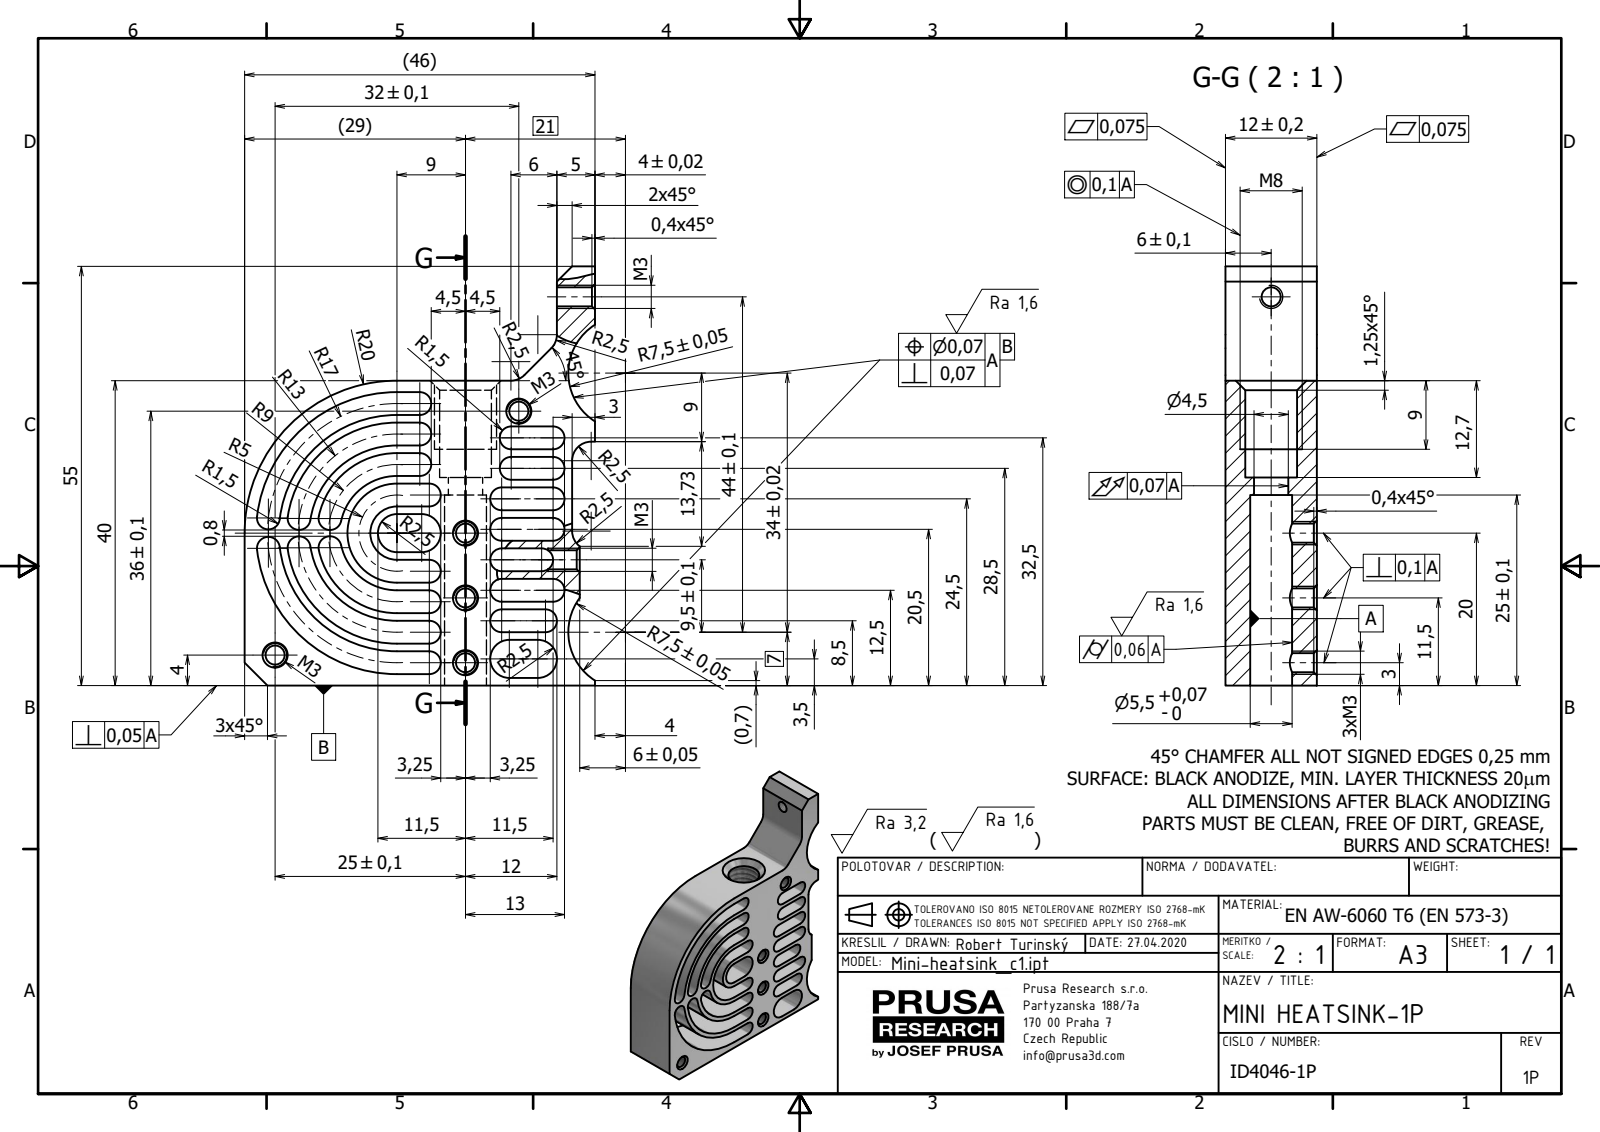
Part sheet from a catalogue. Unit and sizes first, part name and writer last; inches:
Units: inches
Overall size (bounding box): 2.165 × 1.811 × 0.472
Round holes (diameter × count): ⌀0.098 ×7, ⌀0.177 ×1, ⌀0.217 ×1, ⌀0.268 ×1
Partial cylindrical surfaces — rounded edges, fillets, slot ends (radius × count): R0.059 ×26, R0.098 ×4, R0.295 ×3, R0.063 ×2, R0.079 ×2, R0.138 ×1, R0.256 ×1, R0.413 ×1
Main face-to-face distances: 0.472, 0.157, 0.118, 0.315, 0.039, 0.276, 0.197, 0.433, 0.354, 0.63
Hole centre spacings: 0.335, 0.669, 0.687, 0.985, 1.003, 1.028, 1.169, 1.328
Volume: 0.614 in³ · Surface area: 18.73 in²
Bodies: 1 solid, 123 faces (52 planar, 61 cylindrical, 10 other)
Part name (STEP PRODUCT): Mini-heatsink_c1
STEP written by: Autodesk Inventor 2019 (AUTOMOTIVE_DESIGN)
